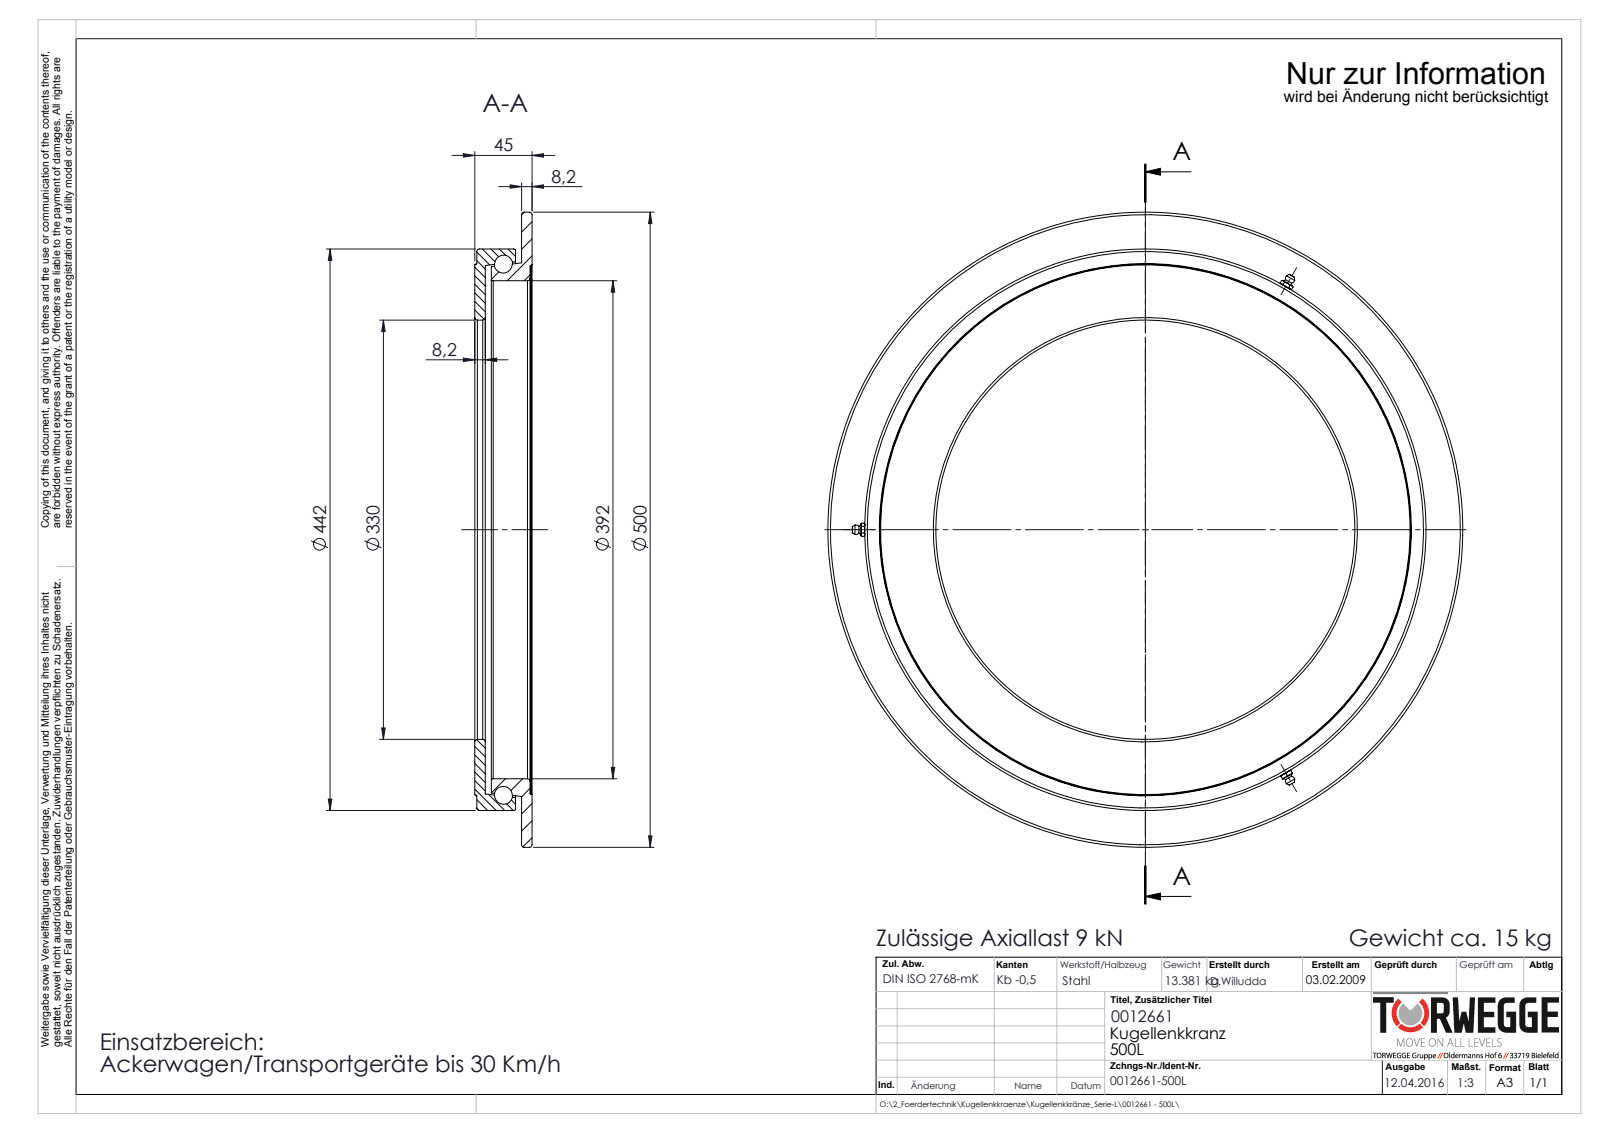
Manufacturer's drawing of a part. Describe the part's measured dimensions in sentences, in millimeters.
The part is named "0012661-500L". Its 3-D file was written by "SolidWorks 2016 (AUTOMOTIVE_DESIGN)". It is 4 solids with 203 faces: 40 planar, 45 cylindrical and 118 other. Overall it measures 500 by 500 by 45 millimeters. Its volume is 1 904 000 cubic millimeters and its surface area 405 859 square millimeters. Round holes: 3 of diameter 1.5, 3 of diameter 4, 3 of diameter 7.5, 2 of diameter 4.9, 1 of diameter 14.5, 1 of diameter 330, 1 of diameter 392, 1 of diameter 416. Round bosses or shafts: 2 of diameter 7.5, 1 of diameter 500, 1 of diameter 442, 1 of diameter 418. Partial cylindrical surfaces (rounded edges, fillets, slot ends): 1 of radius 220.6. The main face-to-face distances are 8.2, 36.8, 45, 28.6, 13, 1.5, 30.5, 32, 4.8, 23.8.
